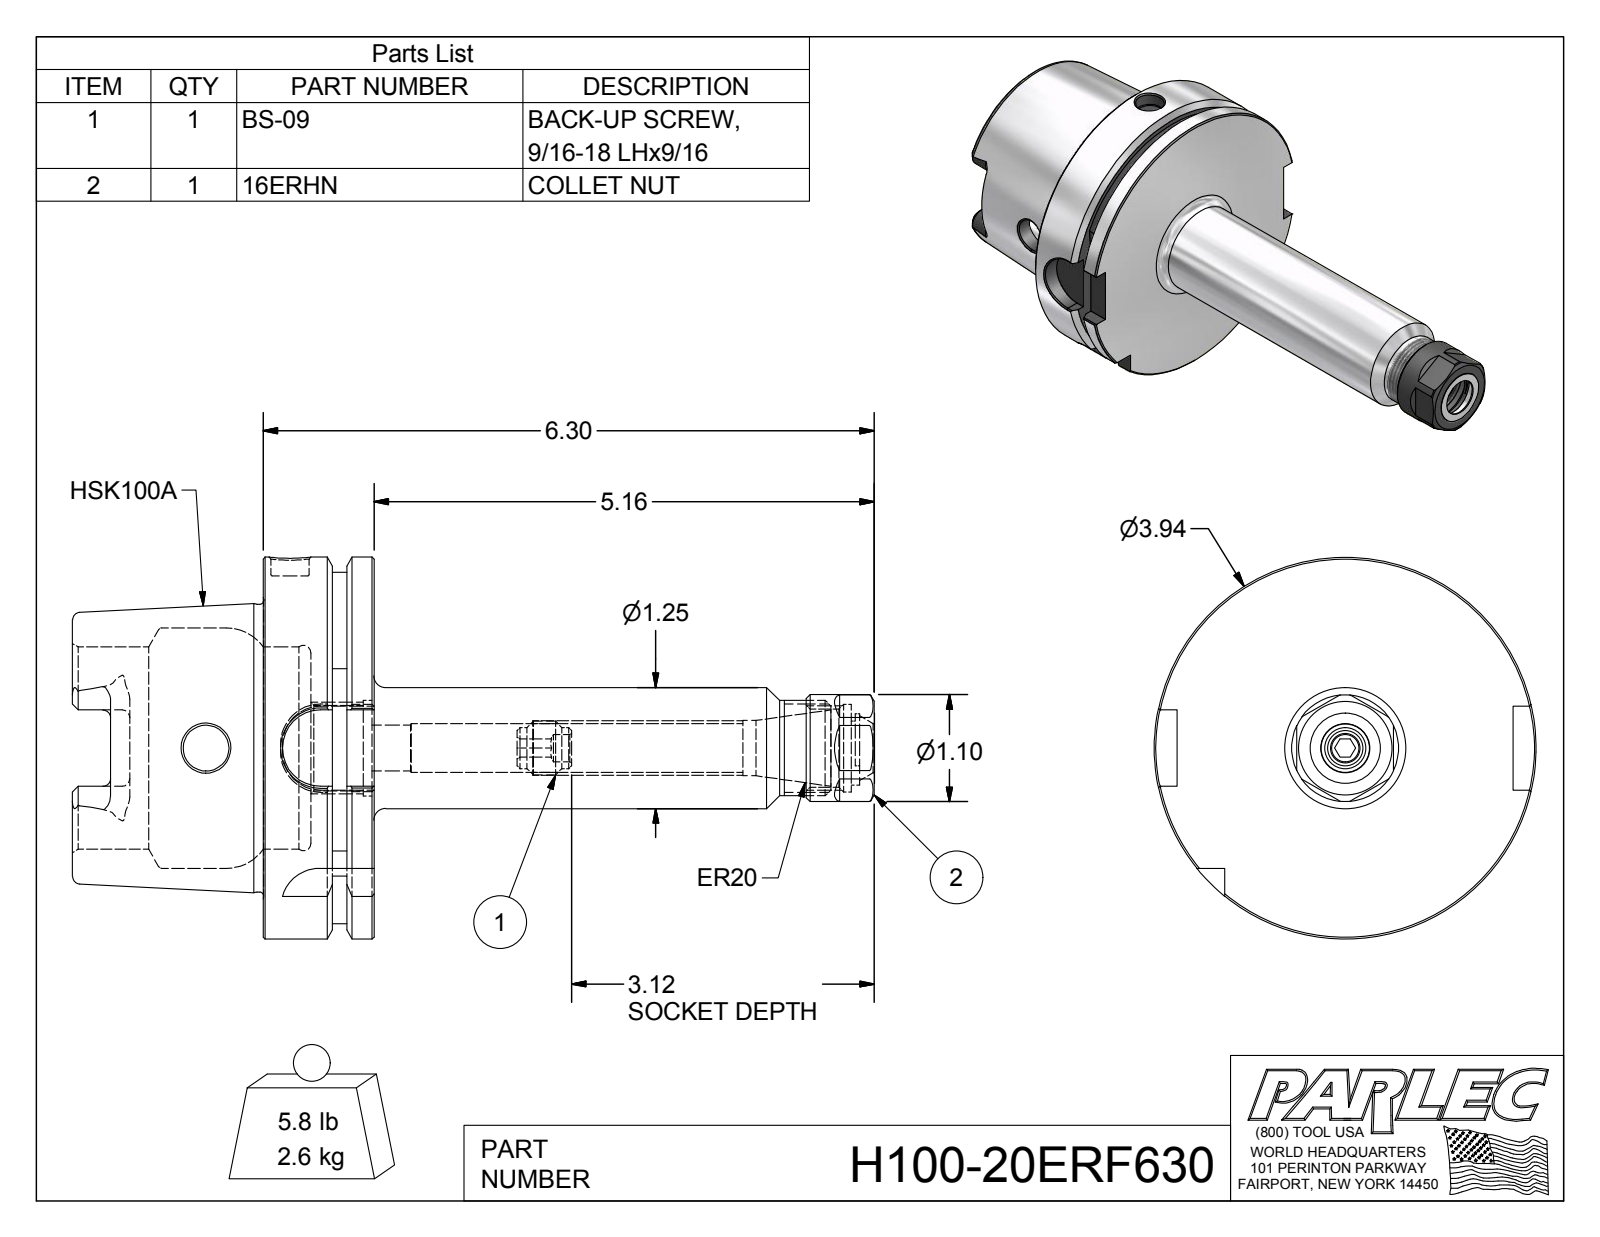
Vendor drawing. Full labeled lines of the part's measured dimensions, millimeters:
Part name (STEP PRODUCT): H100-20ER6-1; 16ERHN; BS-09; H100-20ERF630
STEP written by: Autodesk Inventor 2016 (AUTOMOTIVE_DESIGN)
Units: millimetres
Bodies: 3 solids, 197 faces (74 planar, 50 cylindrical, 73 other)
Overall size (bounding box): 210.02 × 100 × 100
Volume: 385 471 mm³ · Surface area: 72 892 mm²
Round holes (diameter × count): ⌀9 ×2, ⌀12 ×2, ⌀7.14 ×1, ⌀10 ×1, ⌀11.99 ×1, ⌀12.4 ×1, ⌀12.75 ×1, ⌀14.48 ×1, ⌀17.02 ×1, ⌀20.5 ×1, ⌀22.38 ×1, ⌀23 ×1
Round bosses / shafts (diameter × count): ⌀100 ×1, ⌀92 ×1, ⌀75.36 ×1, ⌀49.53 ×1, ⌀31.75 ×1, ⌀28 ×1, ⌀25 ×1, ⌀14.1 ×1
Partial cylindrical surfaces — rounded edges, fillets, slot ends (radius × count): R2 ×6, R4.88 ×4, R10 ×4, R7.24 ×1, R9 ×1
Main face-to-face distances: 29, 12.5, 16.5, 50, 62.5, 79, 125.23, 75.23, 62.73, 46.23
Hole centre spacings: 1.52
